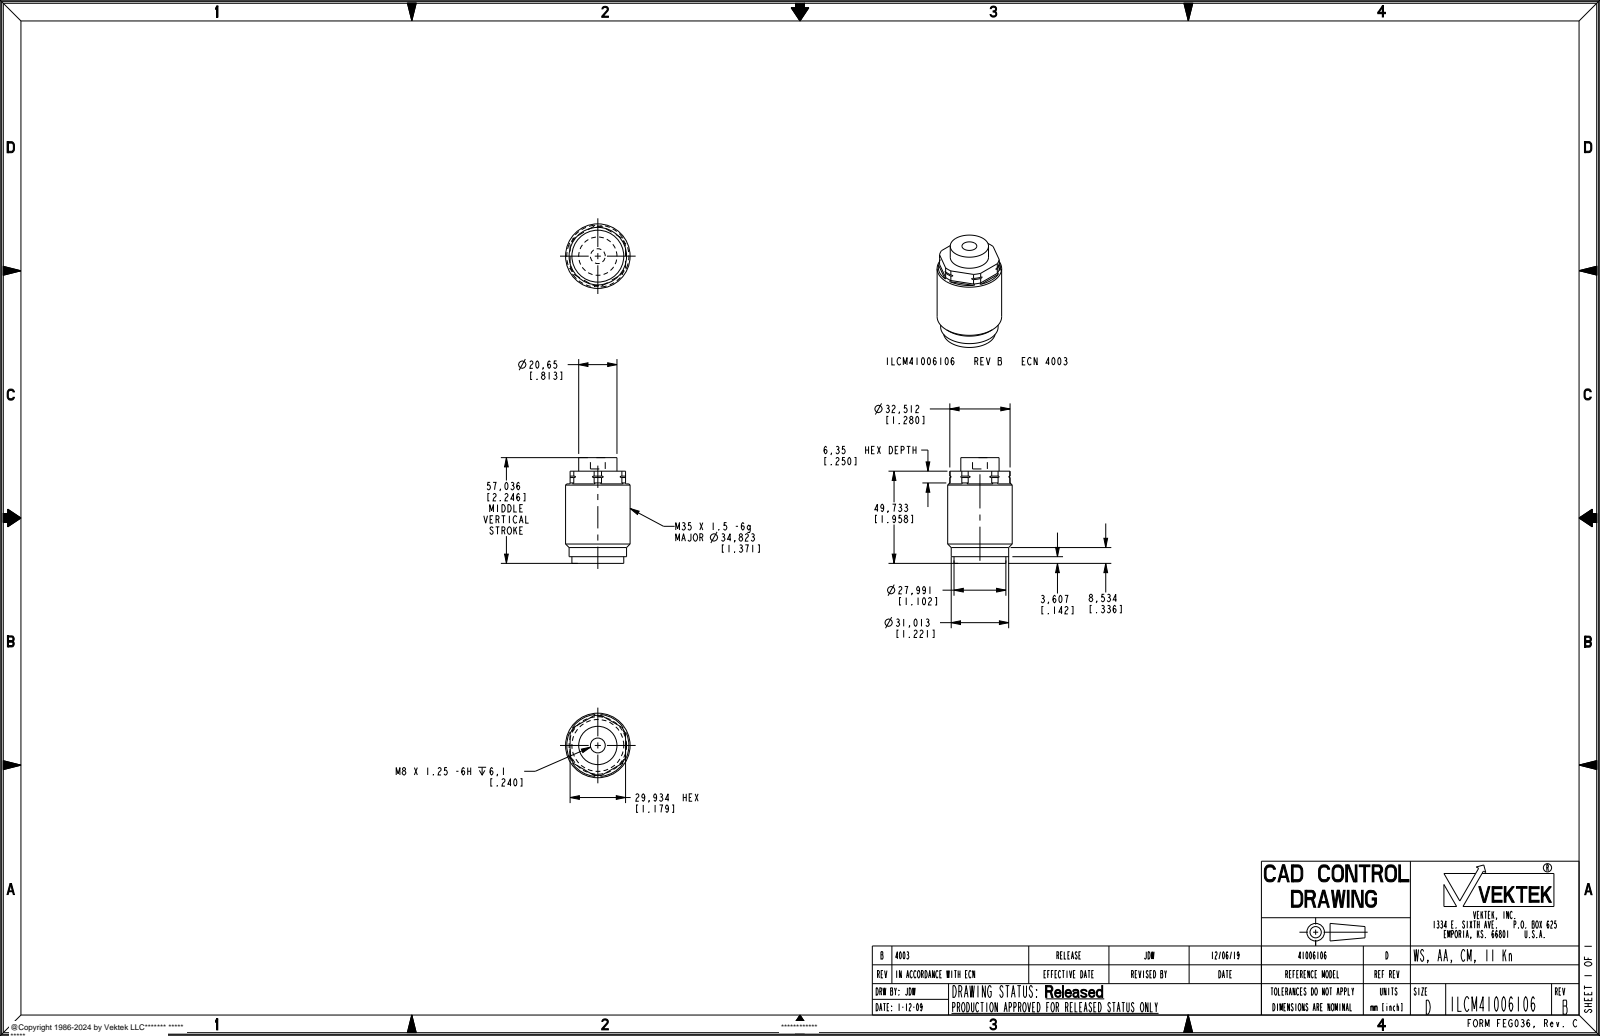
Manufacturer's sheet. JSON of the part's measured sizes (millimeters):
{"part_name": "ILCM41006106", "step_written_by": "PRO/ENGINEER BY PARAMETRIC TECHNOLOGY CORPORATION, 2013320 (AUTOMOTIVE_DESIGN)", "units": "millimeters", "bodies": {"solids": 1, "faces": 55, "planar": 17, "cylindrical": 28, "other": 10}, "overall_size": [57.04, 34.82, 34.82], "volume_mm3": 45815, "surface_area_mm2": 7591, "round_holes": [[8, 1]], "round_bosses_or_shafts": [[34.82, 1], [31.01, 1], [27.99, 1], [20.65, 1]], "partial_cylinders_radius": [[0.51, 6], [16.26, 1]], "face_to_face_distances": [49.73, 57.04, 7.31, 29.94, 3.61, 46.12, 53.43, 42.88, 39.27, 6.85]}
